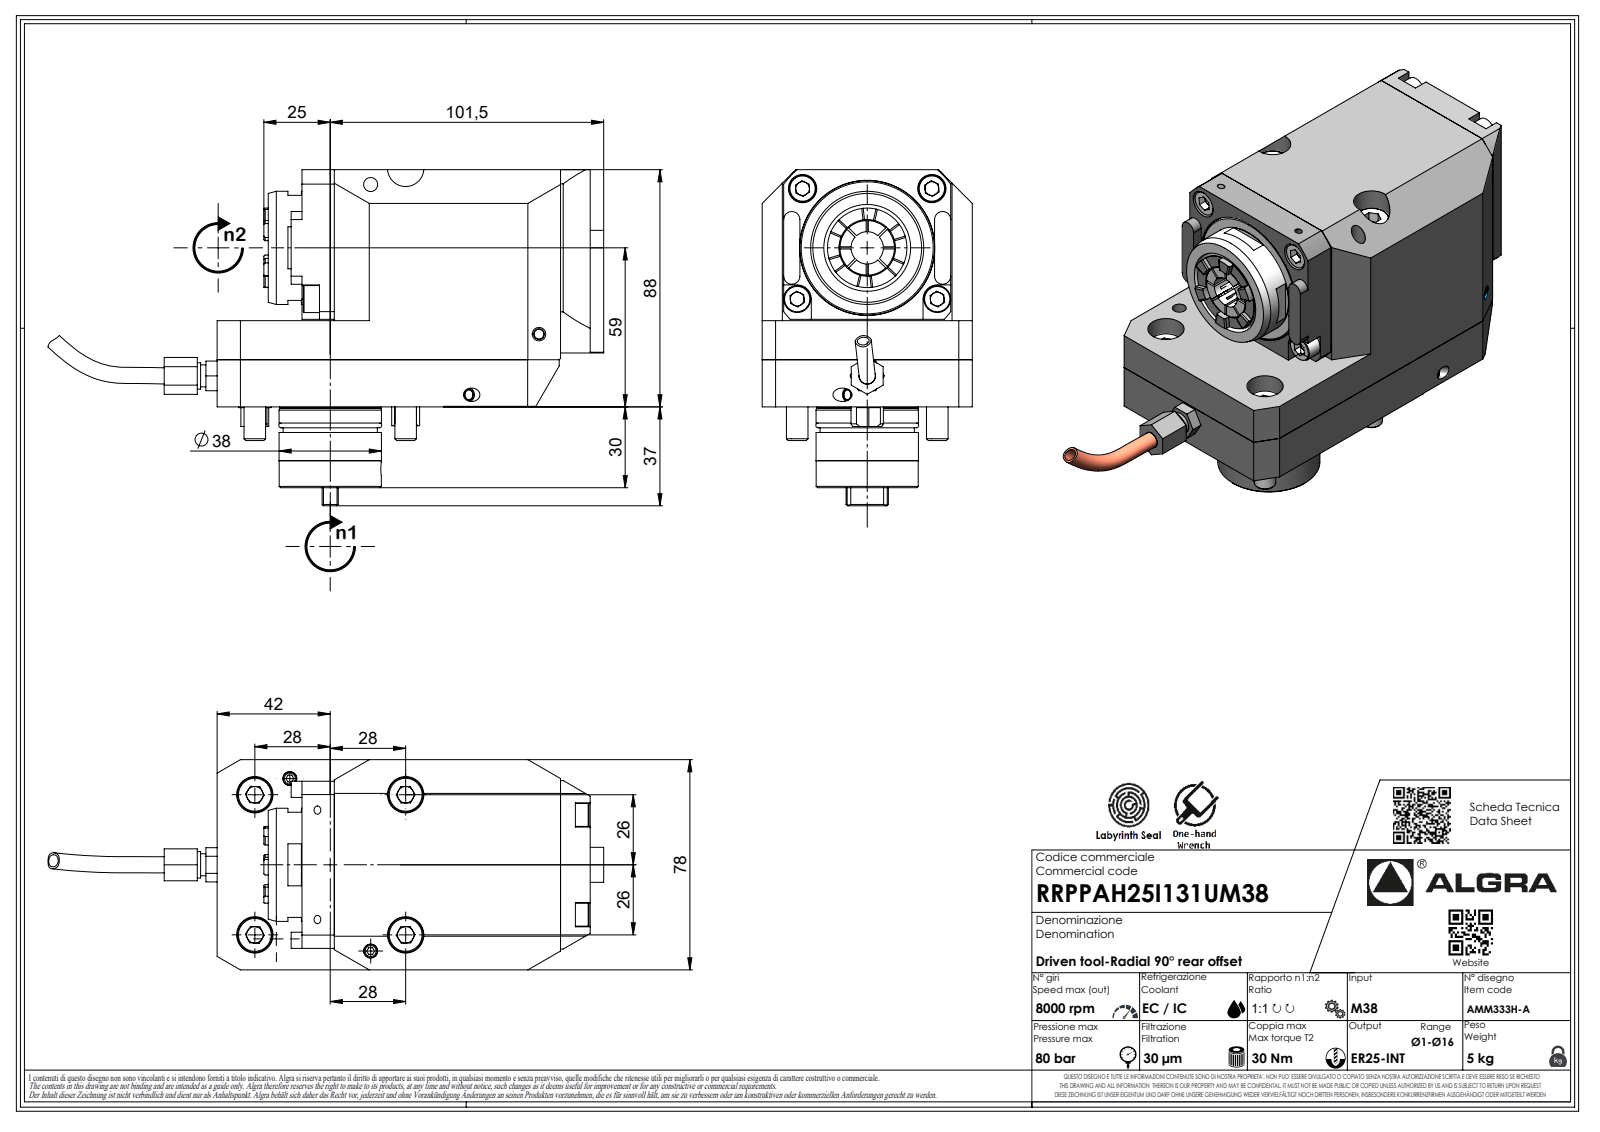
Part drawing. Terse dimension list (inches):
name: RRPPAH25I131UM38
written by: SolidWorks 2023 (AUTOMOTIVE_DESIGN)
unit: in
bodies: 1 solid, 512 faces (342 planar, 58 cylindrical, 112 other)
size: 8.122 × 4.909 × 3.071
volume: 48.65 in³; area: 97.2 in²
holes: 1× ⌀0.083
bosses: 4× ⌀0.315, 1× ⌀1.654, 1× ⌀1.496, 1× ⌀1.492, 1× ⌀1.48, 1× ⌀1.378, 1× ⌀0.472, 1× ⌀0.386
rounds: 7× R0.013, 7× R0.02, 7× R0.146, 4× R0.118, 1× R0.008, 1× R0.236, 1× R0.256, 1× R0.309
face distances: 3.071, 3.465, 2.205, 1.26, 1.252, 3.457, 5.453, 1.24, 4.213, 2.441
